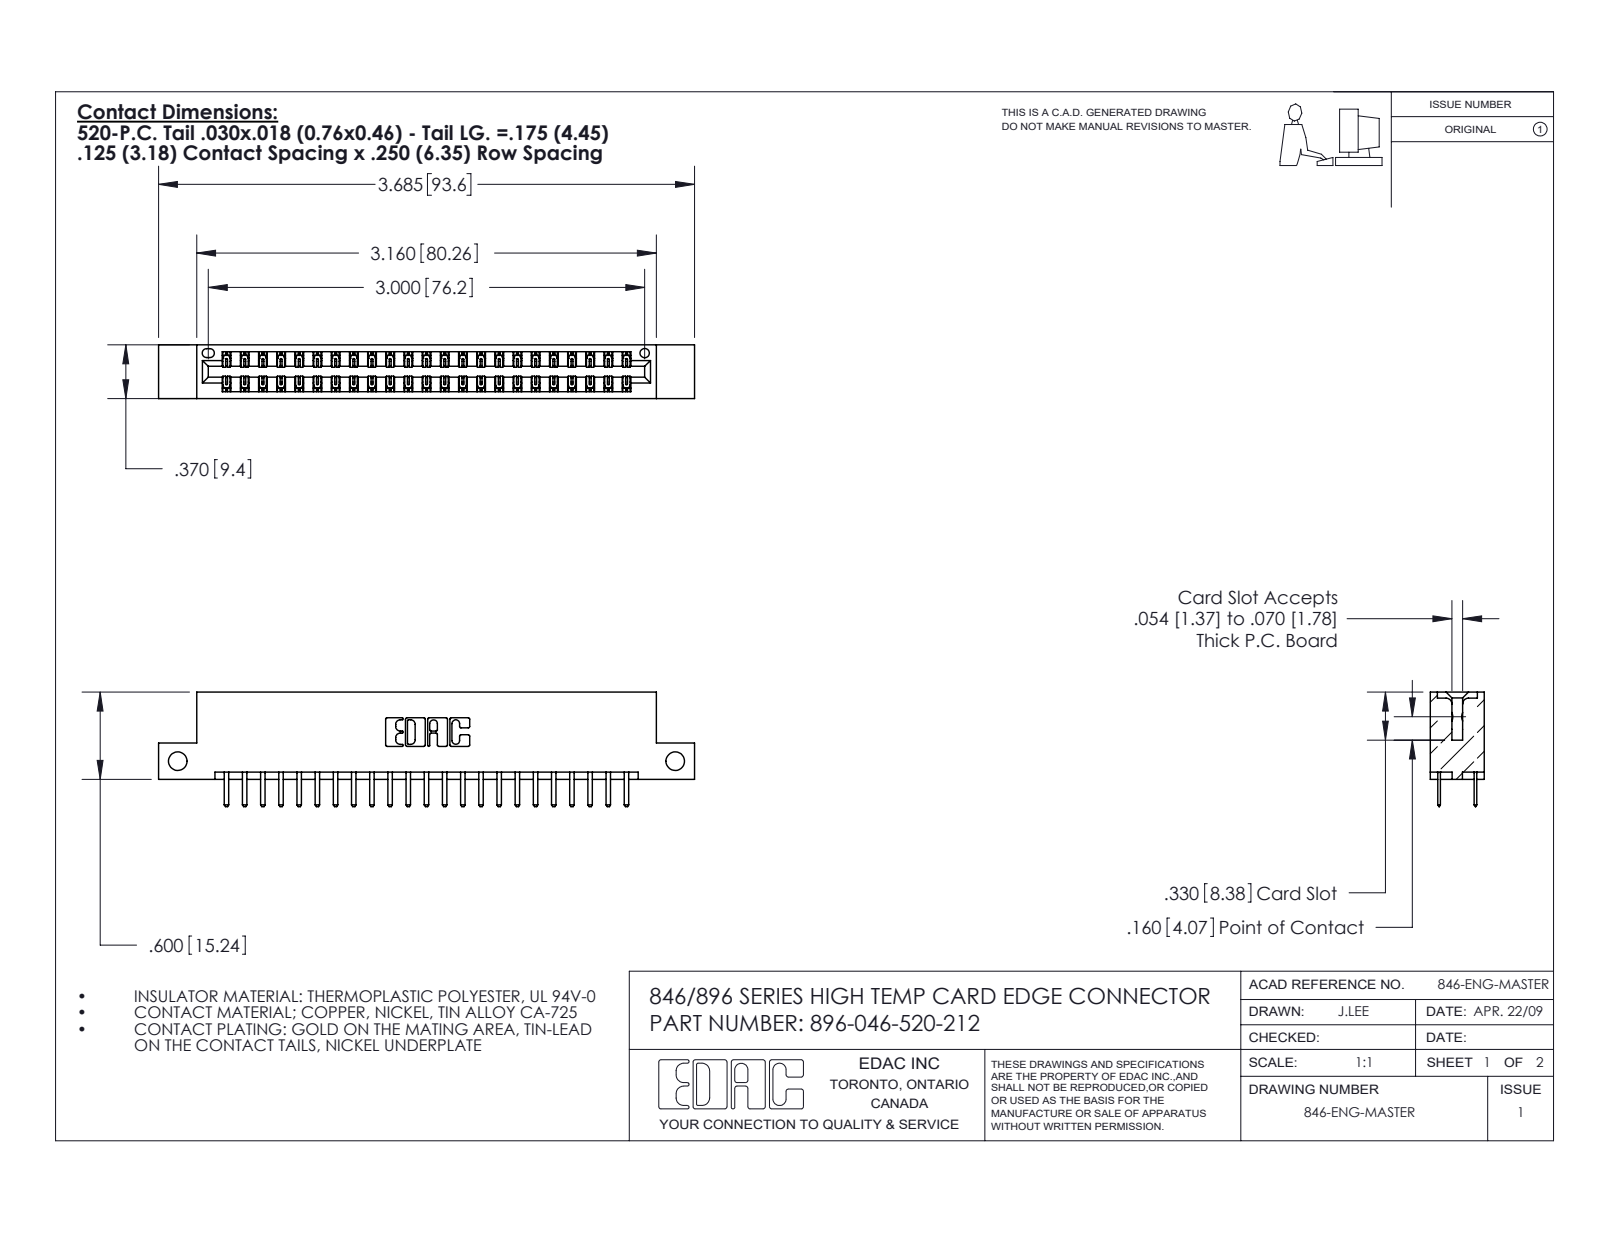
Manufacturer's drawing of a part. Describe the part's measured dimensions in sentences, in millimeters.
The part is named "345-292-001_345-293-120; 396-046-520-212; 346 Part_Flush Mounting Lugs - Side Mount". Its 3-D file was written by "SolidWorks 2016 (CONFIG_CONTROL_DESIGN)". It is 47 solids with 2698 faces: 1778 planar, 920 cylindrical and 0 other. Overall it measures 93.6 by 20 by 9.4 millimeters. Its volume is 8 870 cubic millimeters and its surface area 11 710 square millimeters. Round holes: 2 of diameter 3.3, 1 of diameter 1.6. Partial cylindrical surfaces (rounded edges, fillets, slot ends): 69 of radius 0.2, 50 of radius 0.3, 22 of radius 0.3, 6 of radius 0.2, 6 of radius 0.8, 3 of radius 0.7, 2 of radius 0.4, 2 of radius 0.6. The main face-to-face distances are 6.4, 1.2, 8.2, 9.4, 7, 1.8, 7.6, 0.6, 3.8, 5.6. The hole center spacings are 86.9.
